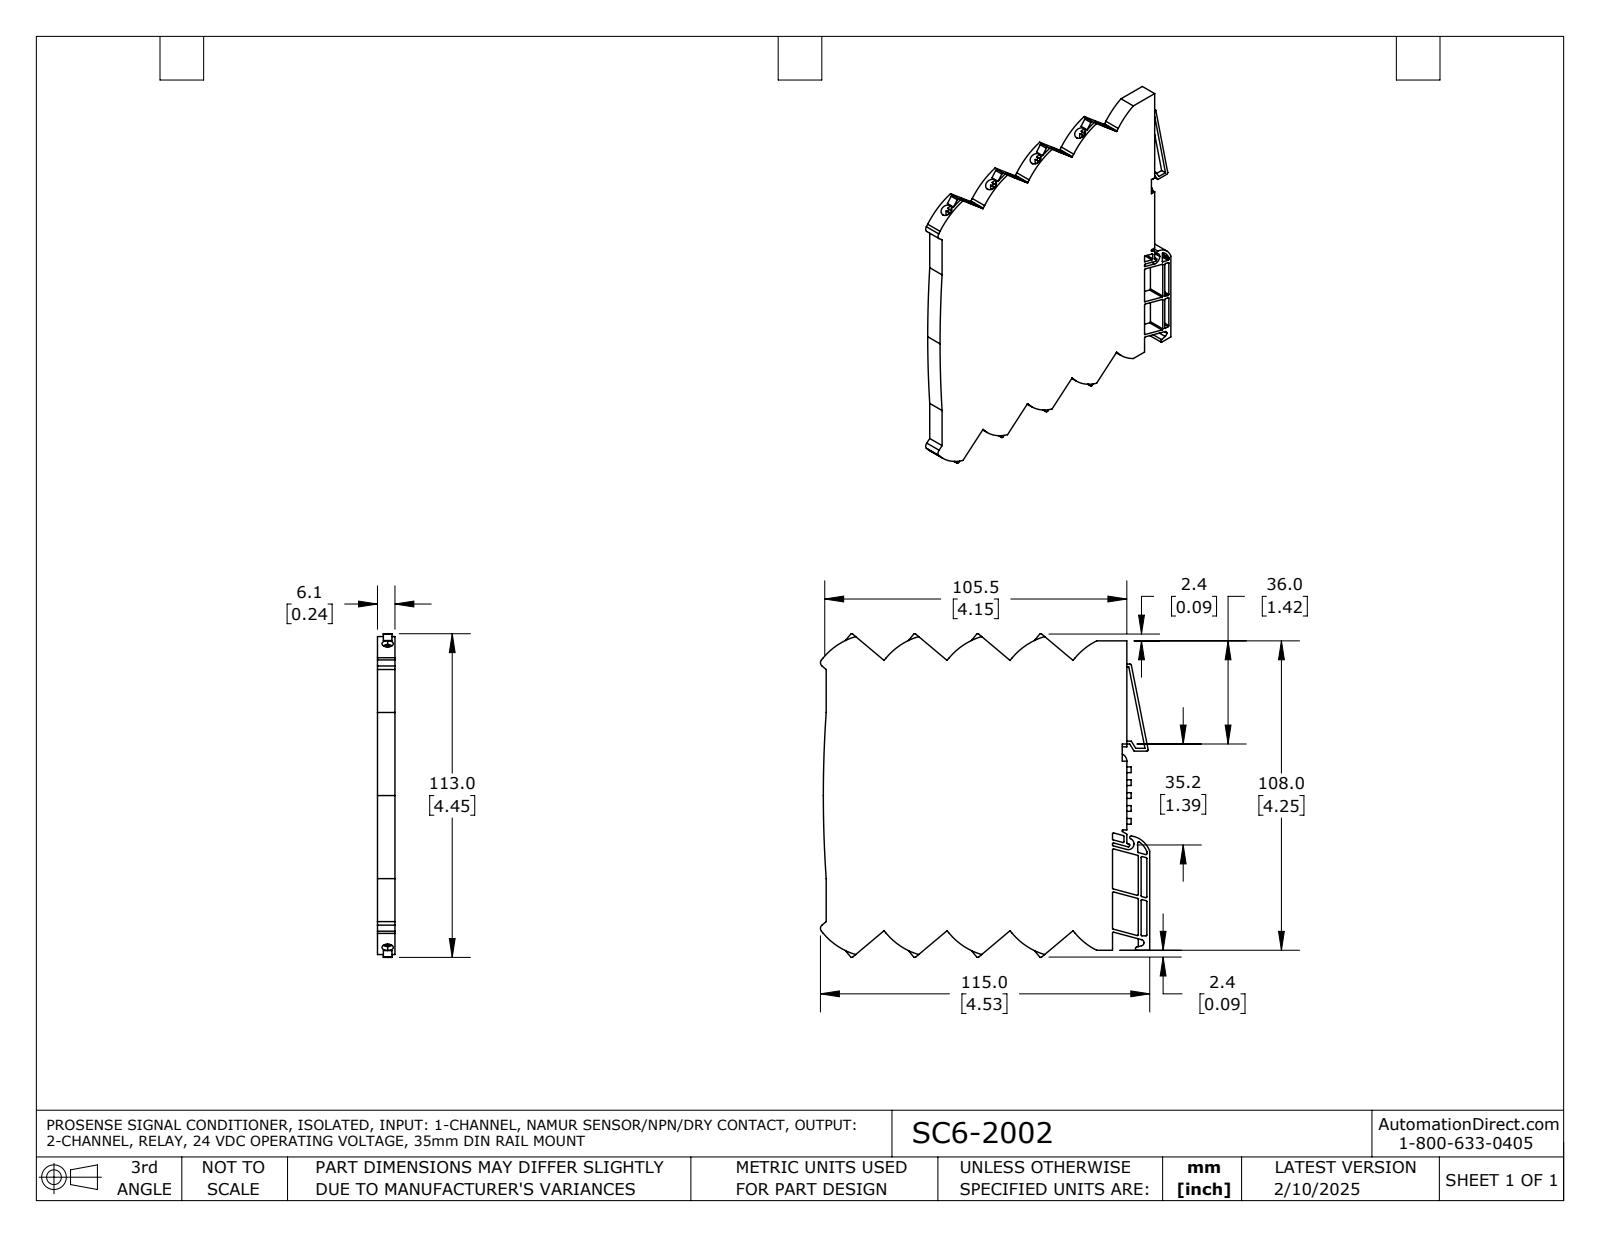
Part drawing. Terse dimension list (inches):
name: SC6-2002
written by: SolidWorks 2021 (AUTOMOTIVE_DESIGN)
unit: in
bodies: 1 solid, 457 faces (333 planar, 124 cylindrical, 0 other)
size: 4.528 × 4.448 × 0.24
volume: 3.996 in³; area: 44.18 in²
holes: 8× ⌀0.157
rounds: 32× R0.012, 11× R0.02, 10× R0.059, 10× R0.918, 1× R0.022, 1× R0.043, 1× R0.058, 1× R0.07
face distances: 0.24, 0.039, 0.118, 0.157, 0.081, 0.557, 0.159, 0.663, 0.041, 0.079
hole spacings: 0.557, 1.114, 0.557, 1.671
